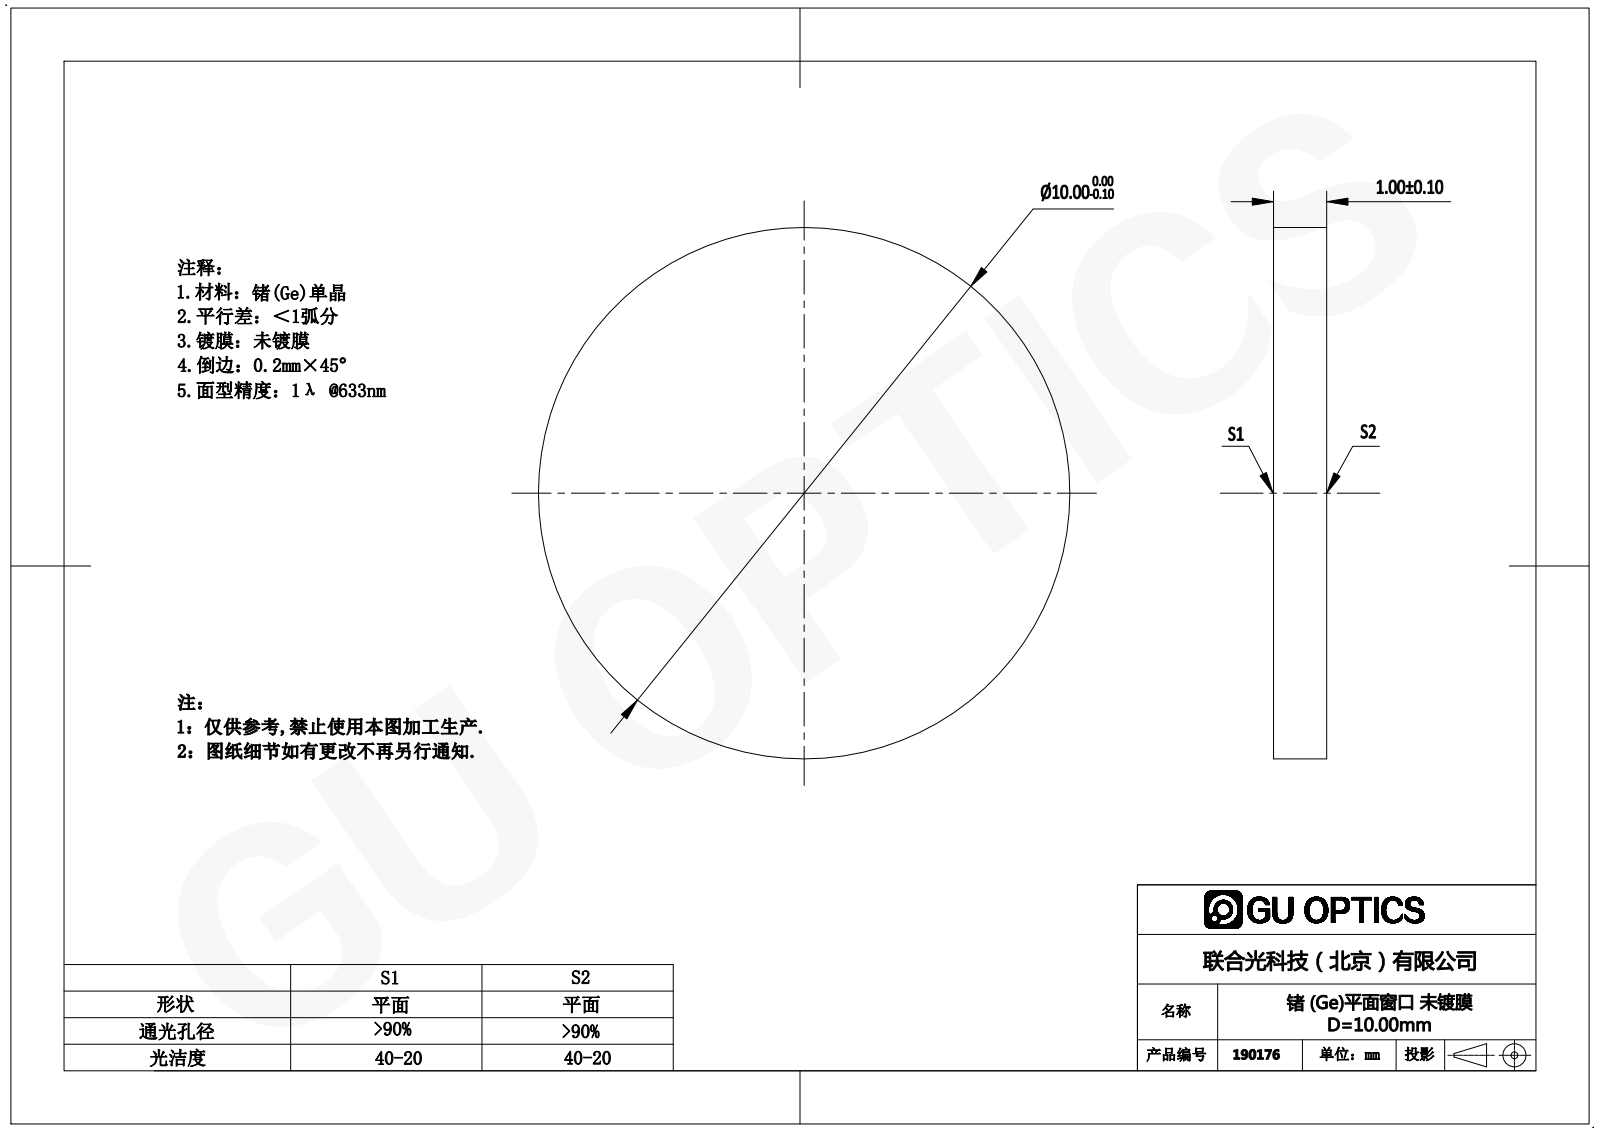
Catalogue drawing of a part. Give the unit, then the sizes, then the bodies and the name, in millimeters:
Units: millimetres
Overall size (bounding box): 10 × 10 × 1
Round bosses / shafts (diameter × count): ⌀10 ×1
Main face-to-face distances: 1
Volume: 79 mm³ · Surface area: 188 mm²
Bodies: 1 solid, 4 faces (2 planar, 2 cylindrical, 0 other)
Part name (STEP PRODUCT): 190162
STEP written by: SolidWorks 2016 (AUTOMOTIVE_DESIGN)
